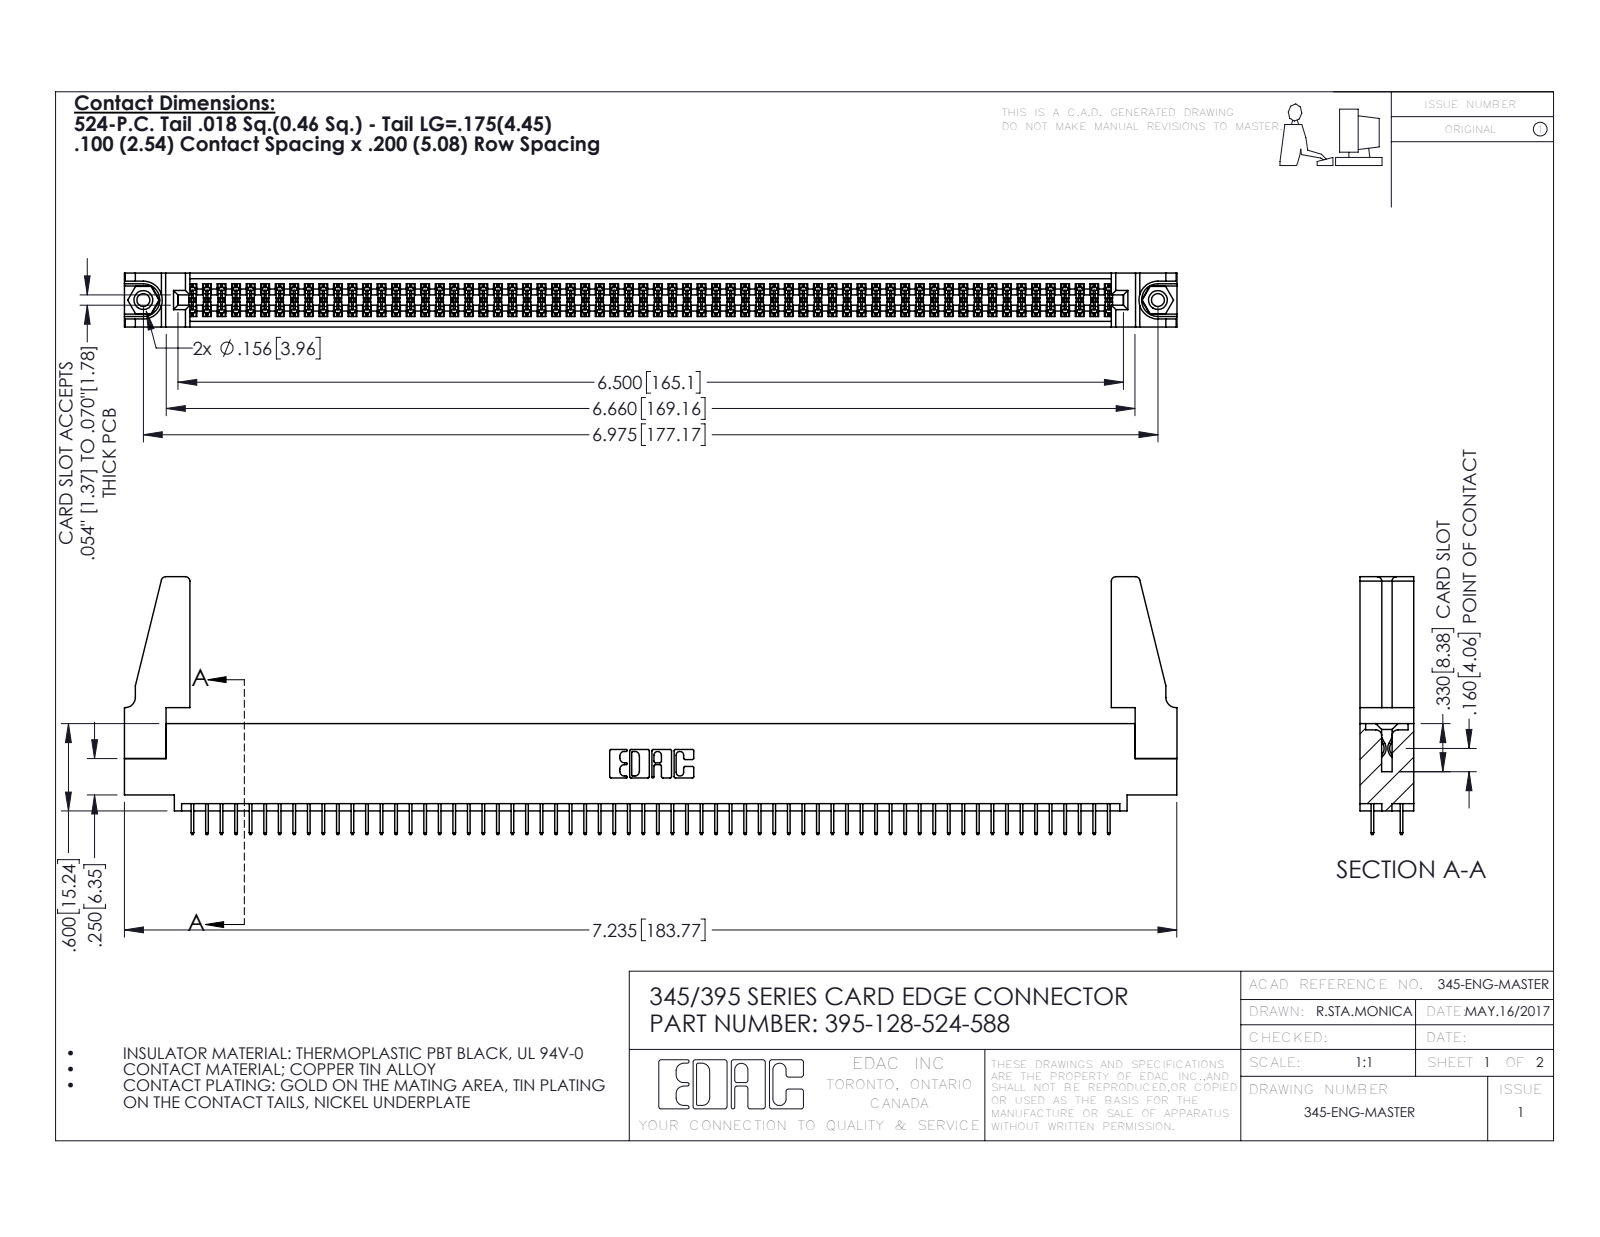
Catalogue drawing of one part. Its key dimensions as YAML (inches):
part_name: "345 Part_0.110 Offset - 0.156 Dia-TH; 345-292-001_345-293-124; 345-250-001_345-250-001-102; 345-220-078_345-220-088 (+1 more)"
step_written_by: "SolidWorks 2016 (CONFIG_CONTROL_DESIGN)"
units: inches
bodies: {solids: 133, faces: 7166, planar: 5148, cylindrical: 2002, other: 16}
overall_size: [7.236, 1.772, 0.37]
volume: 1.284
surface_area: 45.61
round_holes:
  - {diameter: 0.089, count: 2}
  - {diameter: 0.125, count: 2}
  - {diameter: 0.156, count: 2}
  - {diameter: 0.064, count: 1}
round_bosses_or_shafts:
  - {diameter: 0.155, count: 2}
partial_cylinders:
  - {radius: 0.006, count: 192}
  - {radius: 0.01, count: 22}
  - {radius: 0.03, count: 8}
  - {radius: 0.007, count: 6}
  - {radius: 0.031, count: 6}
  - {radius: 0.026, count: 3}
  - {radius: 0.014, count: 2}
  - {radius: 0.019, count: 2}
face_to_face_distances: [0.072, 0.298, 0.37, 0.2, 0.098, 0.272, 0.025, 0.225, 0.072, 0.175]
hole_center_spacings: [0.27, 6.739, 6.975]
